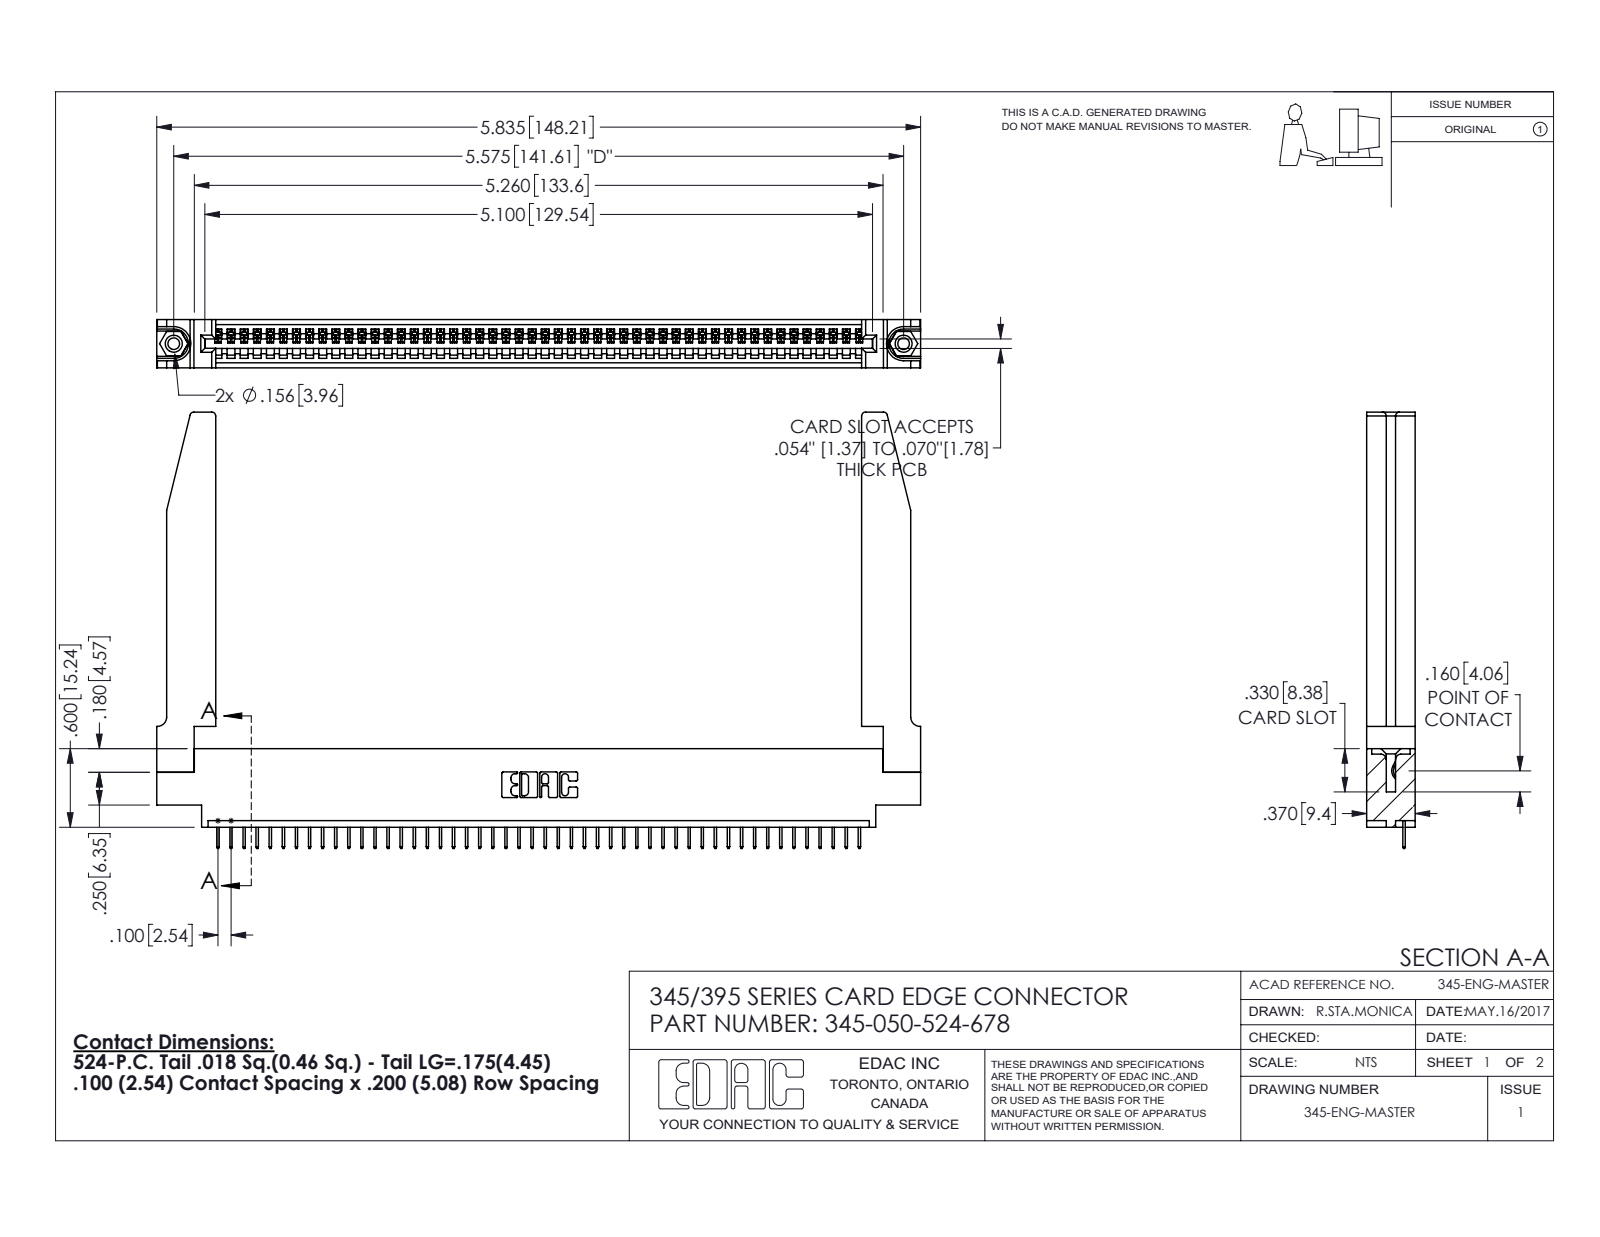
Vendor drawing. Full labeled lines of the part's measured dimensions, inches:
Part name (STEP PRODUCT): 345 Part_0.170 Offset - 0.156 Dia-TH; 345-050-524-678; 345-220-078_345-220-078; 345-250-001_345-250-001-102 (+1 more)
STEP written by: SolidWorks 2016 (CONFIG_CONTROL_DESIGN)
Units: inches
Bodies: 55 solids, 3464 faces (2526 planar, 886 cylindrical, 52 other)
Overall size (bounding box): 5.836 × 3.332 × 0.37
Volume: 1.318 in³ · Surface area: 38.49 in²
Round holes (diameter × count): ⌀0.089 ×2, ⌀0.125 ×2, ⌀0.156 ×2, ⌀0.064 ×1
Round bosses / shafts (diameter × count): ⌀0.155 ×2
Partial cylindrical surfaces — rounded edges, fillets, slot ends (radius × count): R0.006 ×100, R0.01 ×22, R0.03 ×8, R0.007 ×6, R0.031 ×6, R0.026 ×3, R0.031 ×2, R0.04 ×2
Main face-to-face distances: 0.37, 0.072, 0.298, 0.098, 0.272, 0.025, 0.2, 0.225, 0.15, 0.148
Hole centre spacings: 0.27, 5.339, 5.575
